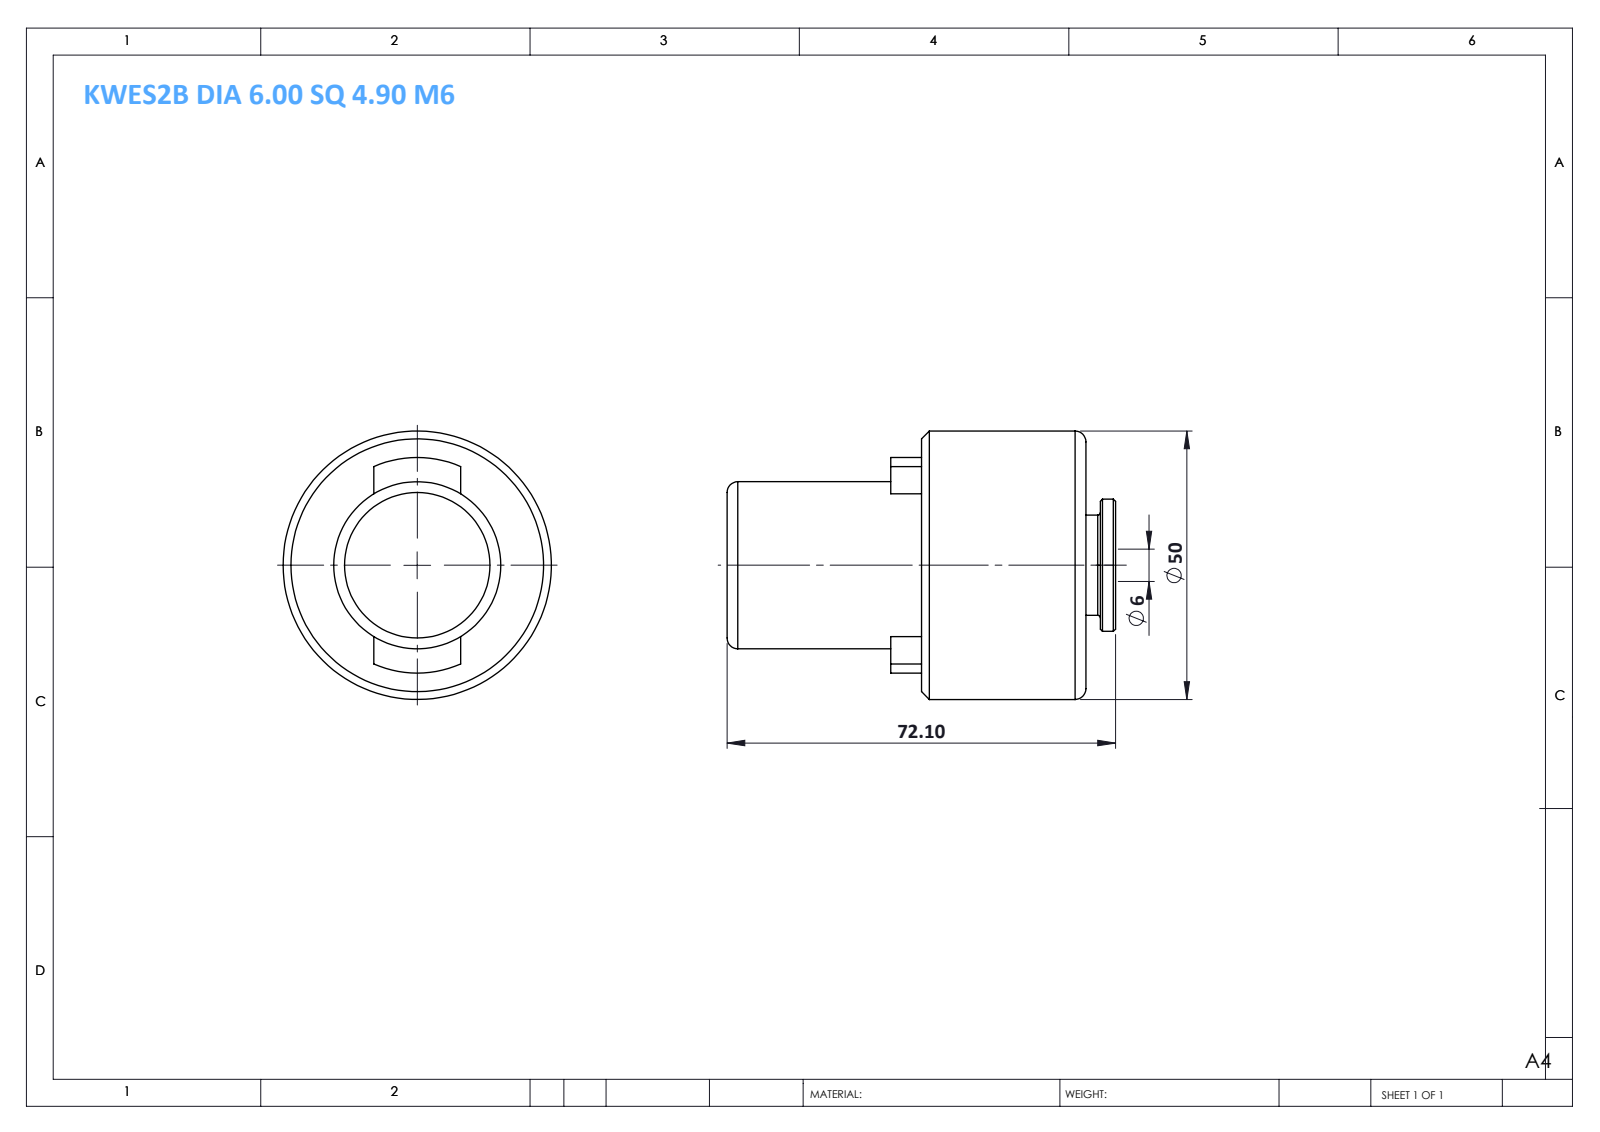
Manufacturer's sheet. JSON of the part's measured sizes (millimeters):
{"part_name": "KWES2B DIA 6.00 SQ 4.90 M5", "step_written_by": "SolidWorks 2014 (CONFIG_CONTROL_DESIGN)", "units": "millimeters", "bodies": {"solids": 1, "faces": 38, "planar": 12, "cylindrical": 12, "other": 14}, "overall_size": [72.1, 49.8, 49.8], "volume_mm3": 88419, "surface_area_mm2": 13165, "round_holes": [[6, 1]], "round_bosses_or_shafts": [[49.8, 1], [31, 1], [24.5, 1], [18.6, 1]], "partial_cylinders_radius": [[20, 1]], "face_to_face_distances": [30.5, 36.1, 66.6, 72.1, 36, 5.5, 30.4, 5.7, 36.2, 41.7]}
